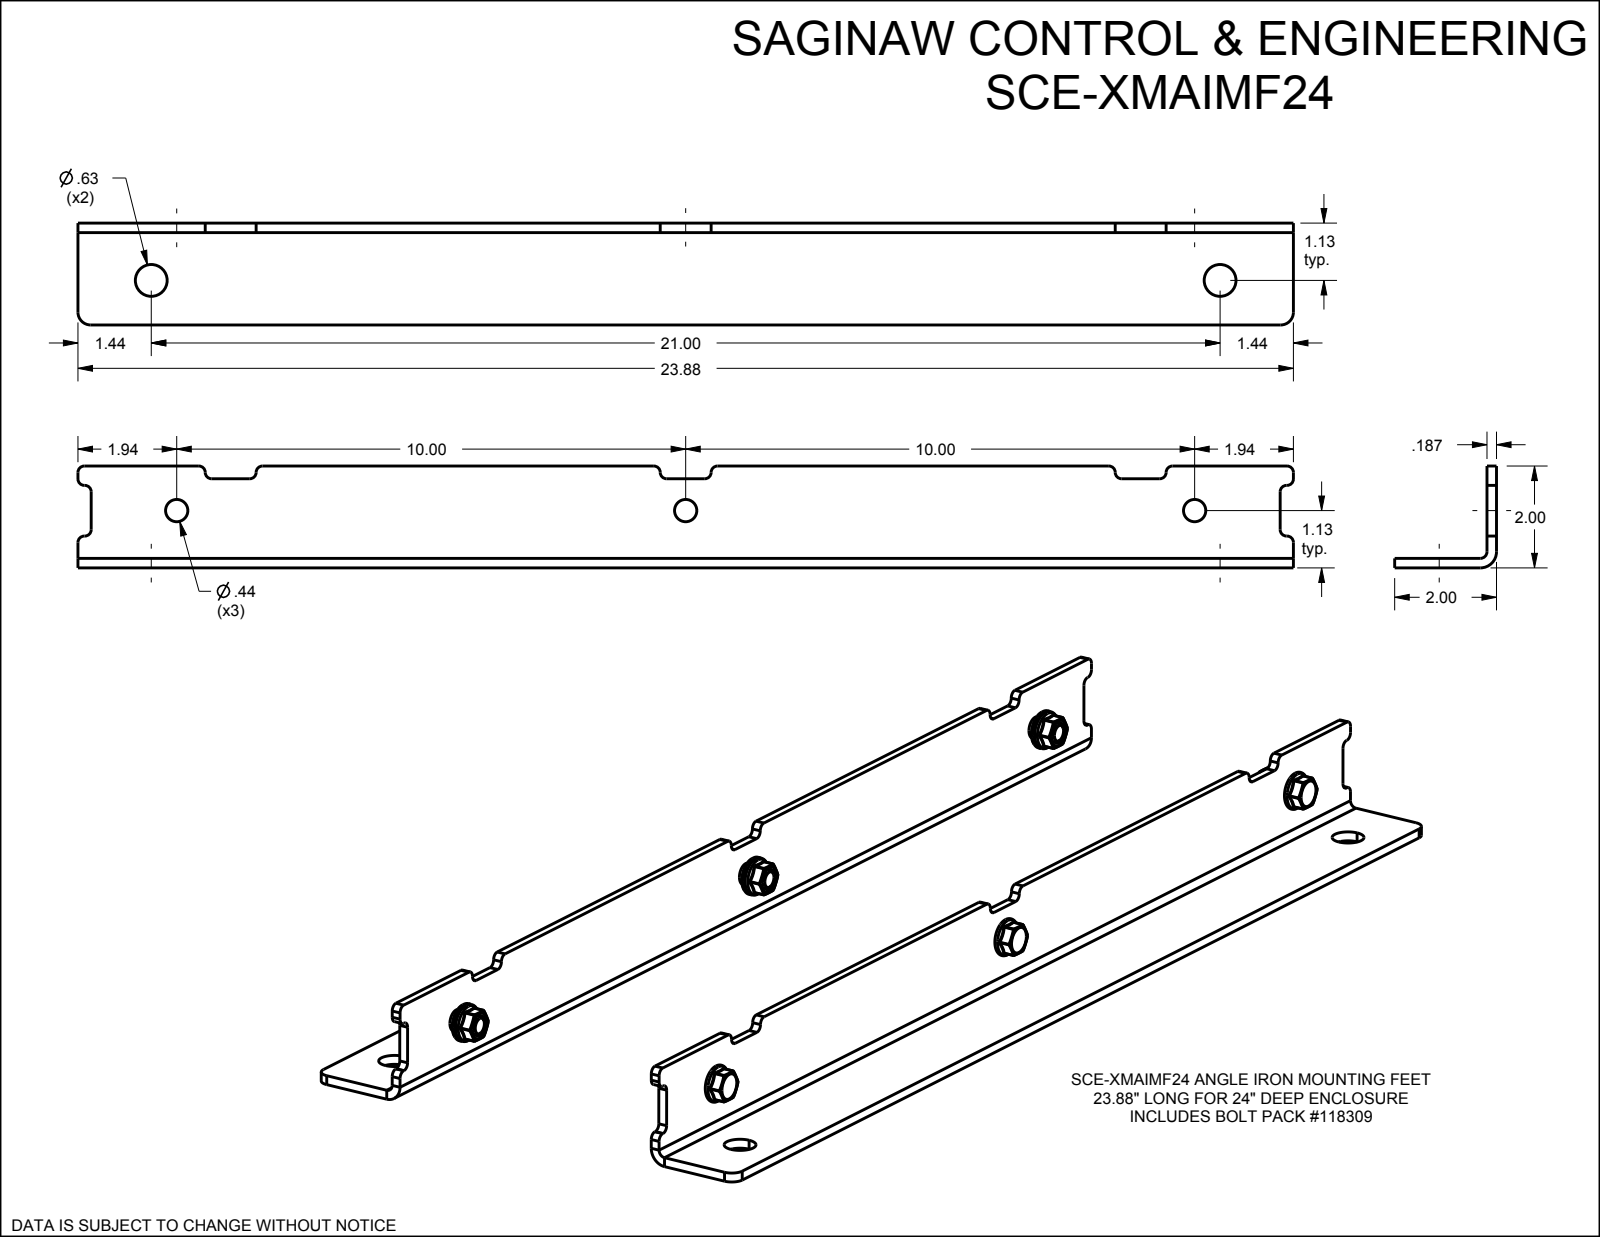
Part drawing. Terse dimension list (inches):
name: SCE-XMAIMF24
written by: SolidWorks 2019 (CONFIG_CONTROL_DESIGN)
unit: in
bodies: 20 solids, 682 faces (170 planar, 170 cylindrical, 342 other)
size: 23.875 × 10 × 2
volume: 33.94 in³; area: 398.1 in²
holes: 4× ⌀0.625, 3× ⌀0.367, 3× ⌀0.4, 3× ⌀0.43, 3× ⌀0.437
bosses: 3× ⌀0.75, 3× ⌀0.7, 3× ⌀0.373
rounds: 30× R0.01, 28× R0.125, 4× R0.25, 2× R0.13, 2× R0.317
face distances: 0.187, 6.187, 6.374, 6, 1.813, 2, 8, 8.187, 10.001, 2.223
hole spacings: 8.25, 10, 20.995, 22.558, 9.995, 9.997, 9.998, 10.003
